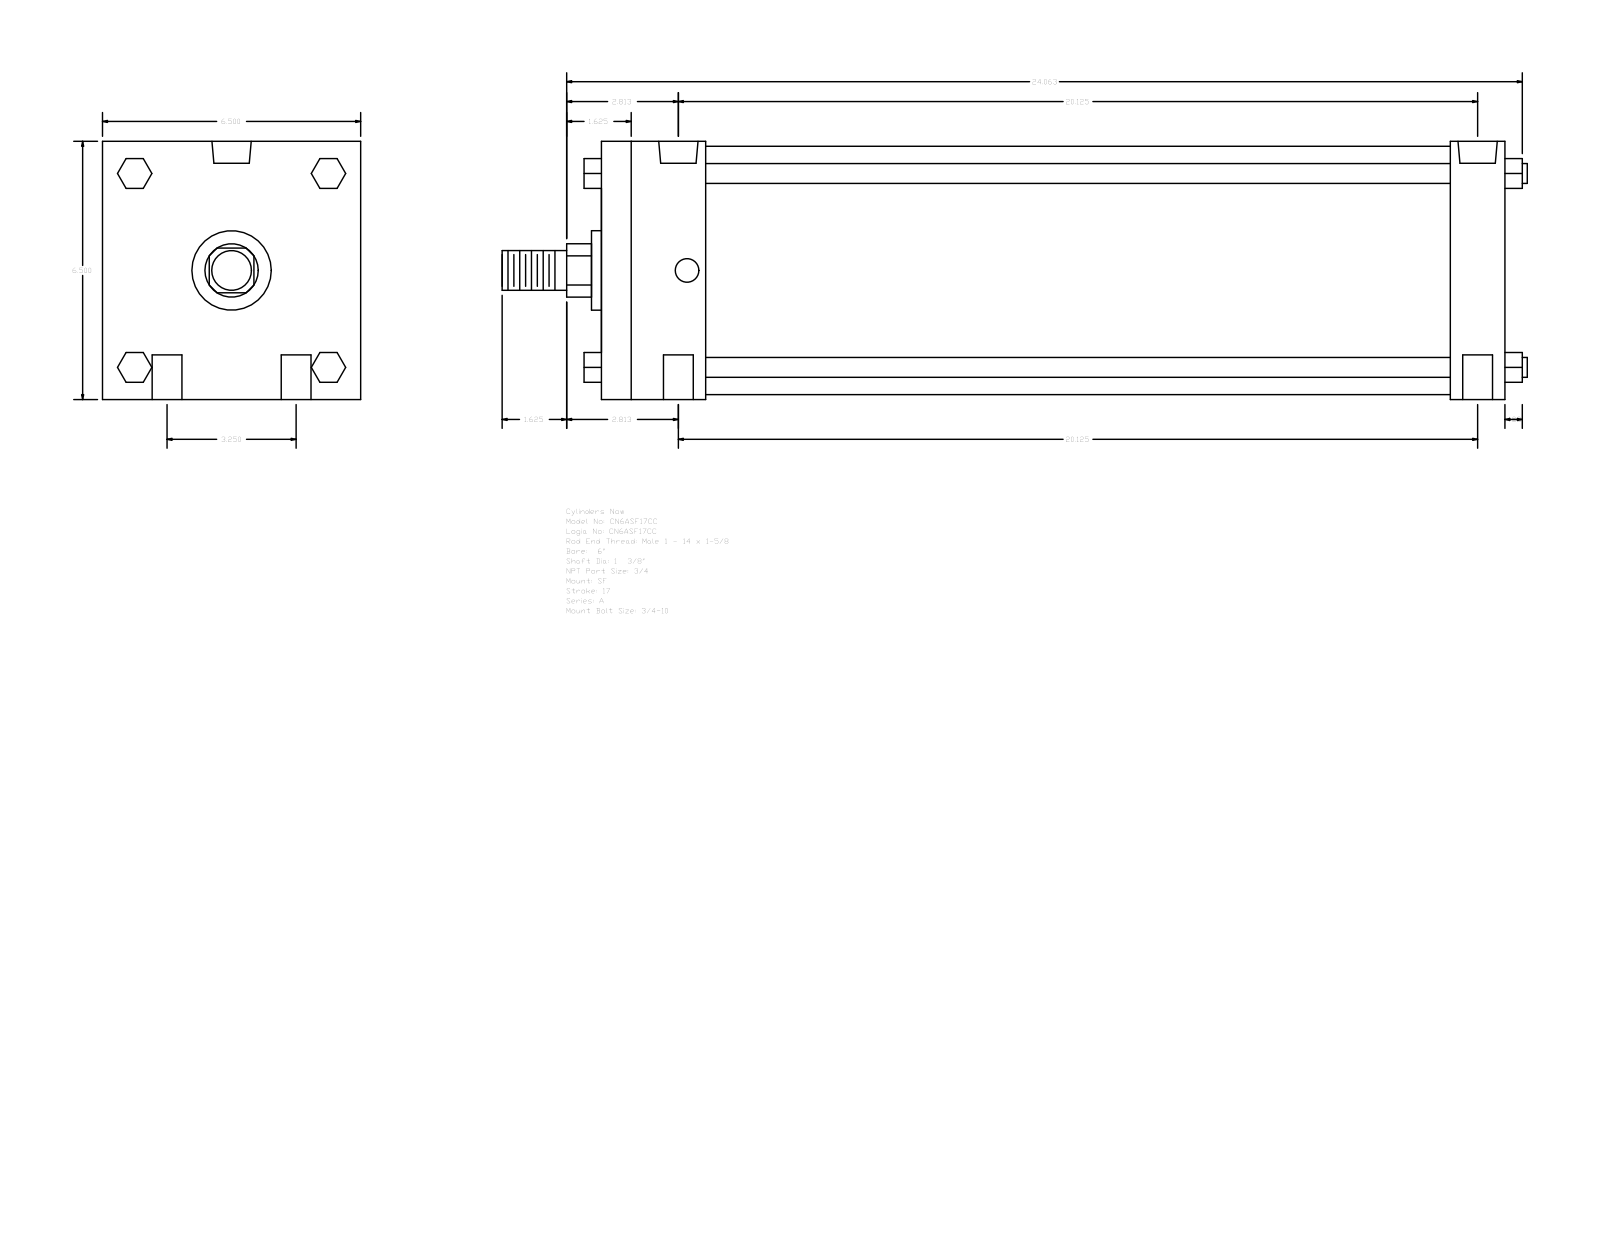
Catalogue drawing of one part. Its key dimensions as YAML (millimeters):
part_name: "A_SF__0600_1.375"
step_written_by: "GSSL Pune (CONFIG_CONTROL_DESIGN)"
units: millimeters
bodies: {solids: 0, faces: 124, planar: 94, cylindrical: 30, other: 0}
overall_size: [655.64, 165.1, 165.1]
round_holes:
  - {diameter: 19.05, count: 4}
  - {diameter: 15.08, count: 2}
  - {diameter: 25.12, count: 2}
round_bosses_or_shafts:
  - {diameter: 12.7, count: 4}
  - {diameter: 158.75, count: 1}
  - {diameter: 50.8, count: 1}
  - {diameter: 34.92, count: 1}
  - {diameter: 25.4, count: 1}
partial_cylinders:
  - {radius: 17.06, count: 1}
face_to_face_distances: [165.1, 577.85, 542.92, 34.93, 66.67, 476.25, 511.18, 19.05, 61.97, 107.34]
hole_center_spacings: [41.27, 512.83, 511.17, 82.54, 517.79, 500.05]
